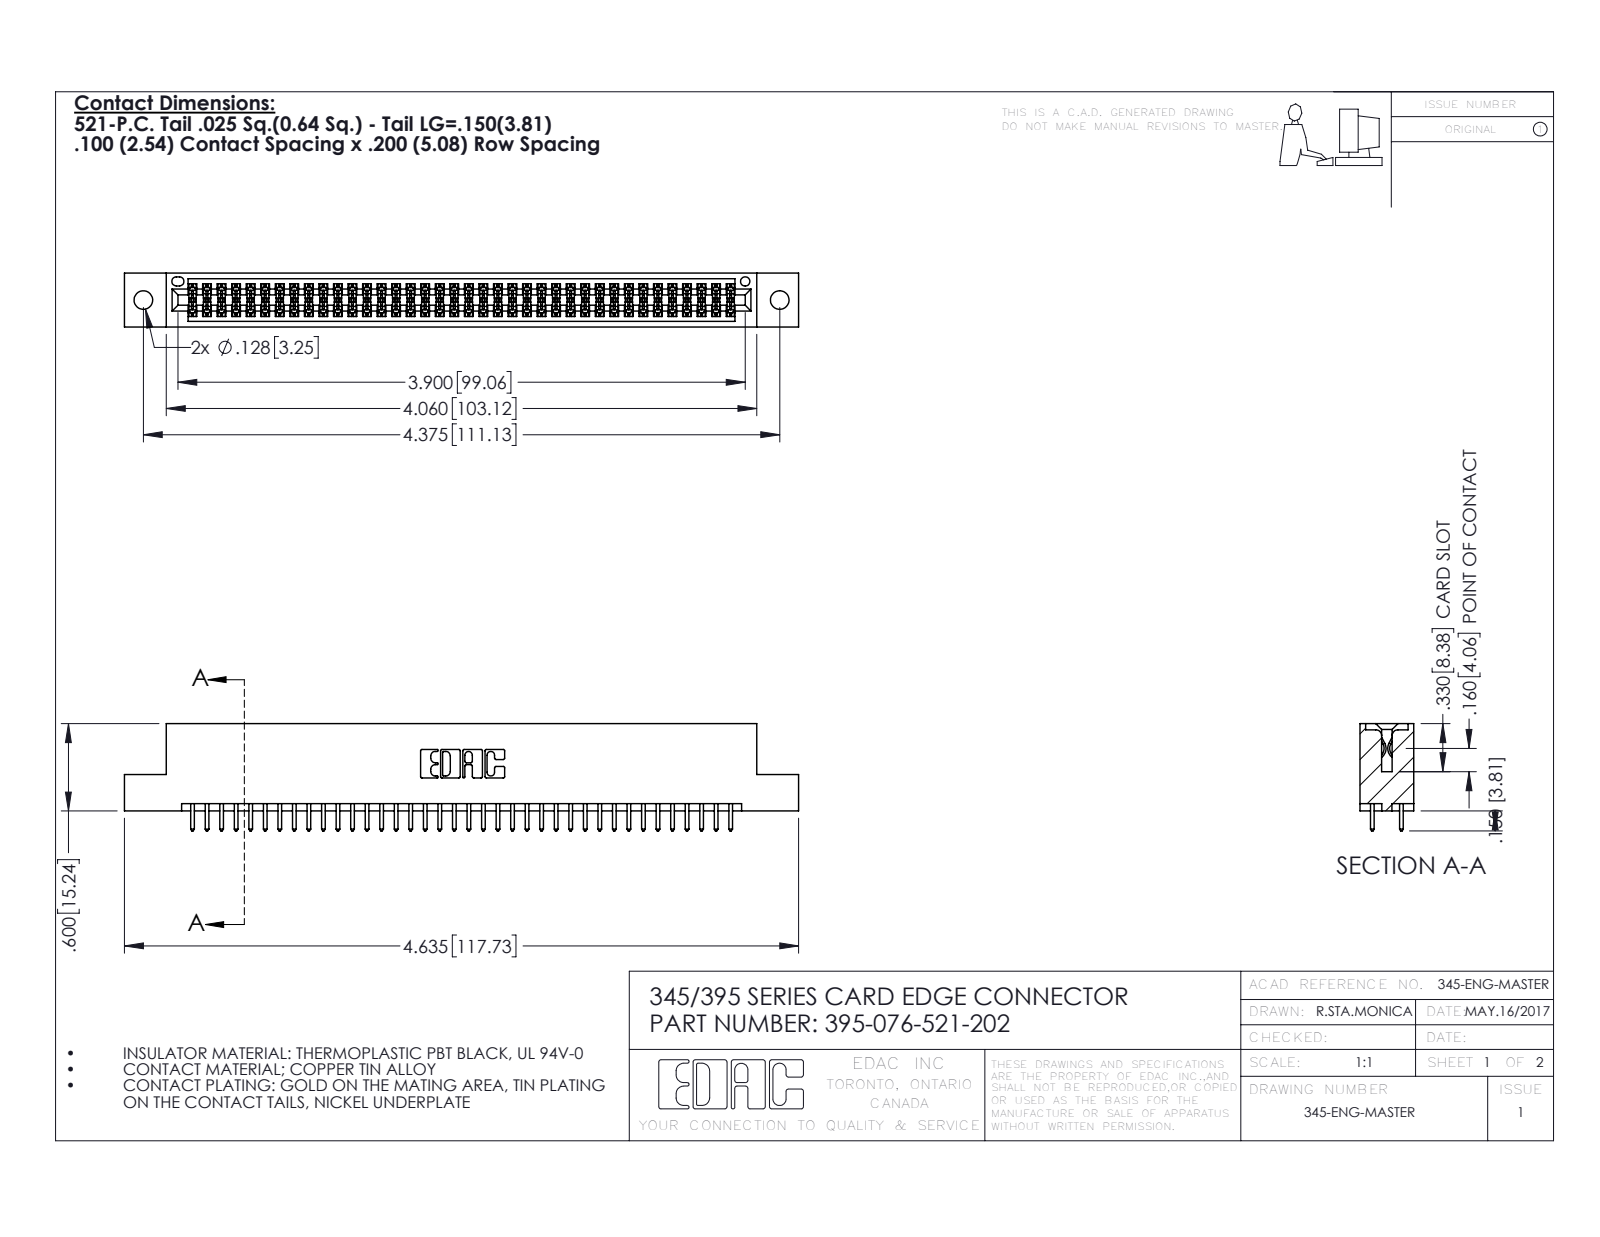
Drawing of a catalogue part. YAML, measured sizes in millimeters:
part_name: "345-292-001_345-293-121; 395-076-521-202; 345 Part_Flush Mounting Lugs - 0.128 Dia"
step_written_by: "SolidWorks 2016 (CONFIG_CONTROL_DESIGN)"
units: millimeters
bodies: {solids: 77, faces: 3926, planar: 2588, cylindrical: 1338, other: 0}
overall_size: [117.7, 18.7, 9.4]
volume: 11300
surface_area: 16200
round_holes:
  - {diameter: 3.3, count: 2}
  - {diameter: 1.6, count: 1}
partial_cylinders:
  - {radius: 0.2, count: 114}
  - {radius: 0.3, count: 76}
  - {radius: 0.3, count: 22}
  - {radius: 0.2, count: 6}
  - {radius: 0.8, count: 6}
  - {radius: 0.7, count: 3}
  - {radius: 0.4, count: 2}
  - {radius: 0.5, count: 2}
face_to_face_distances: [7.6, 1.8, 5.1, 9.4, 2.5, 6.9, 0.6, 5.7, 4.4, 3.8]
hole_center_spacings: [6.9, 105.1, 111.1]
